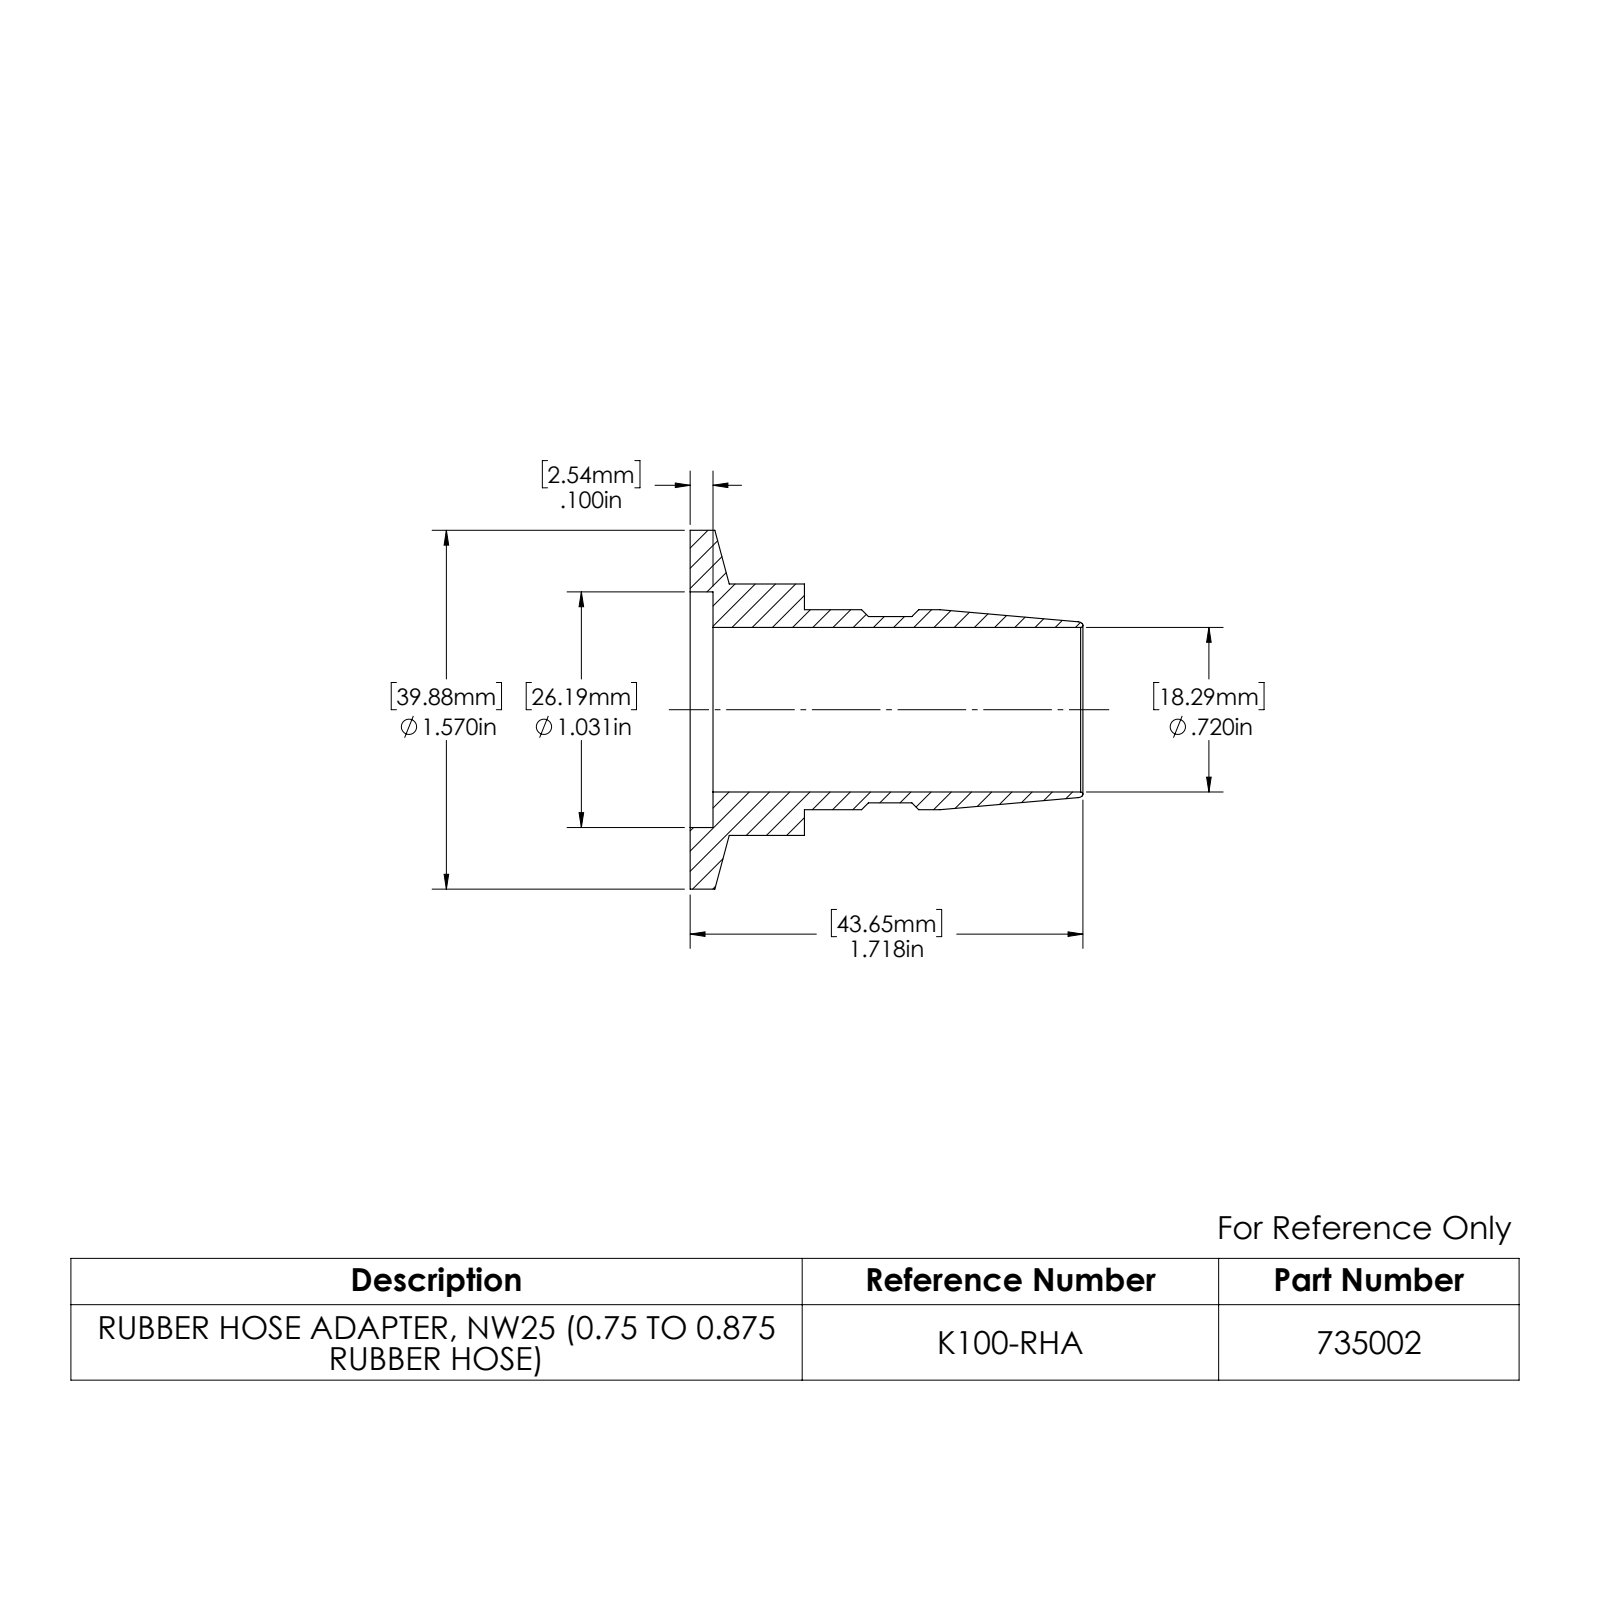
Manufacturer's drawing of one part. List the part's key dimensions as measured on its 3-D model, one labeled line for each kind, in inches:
Part name (STEP PRODUCT): 735002
STEP written by: SolidWorks 2022 (AUTOMOTIVE_DESIGN)
Units: inches
Bodies: 1 solid, 29 faces (3 planar, 14 cylindrical, 12 other)
Overall size (bounding box): 1.718 × 1.57 × 1.57
Volume: 0.538 in³ · Surface area: 11.85 in²
Round holes (diameter × count): ⌀0.72 ×1, ⌀1.031 ×1
Round bosses / shafts (diameter × count): ⌀1.57 ×1, ⌀1.1 ×1, ⌀0.875 ×1, ⌀0.815 ×1
Main face-to-face distances: 0.1, 0.5, 0.4
